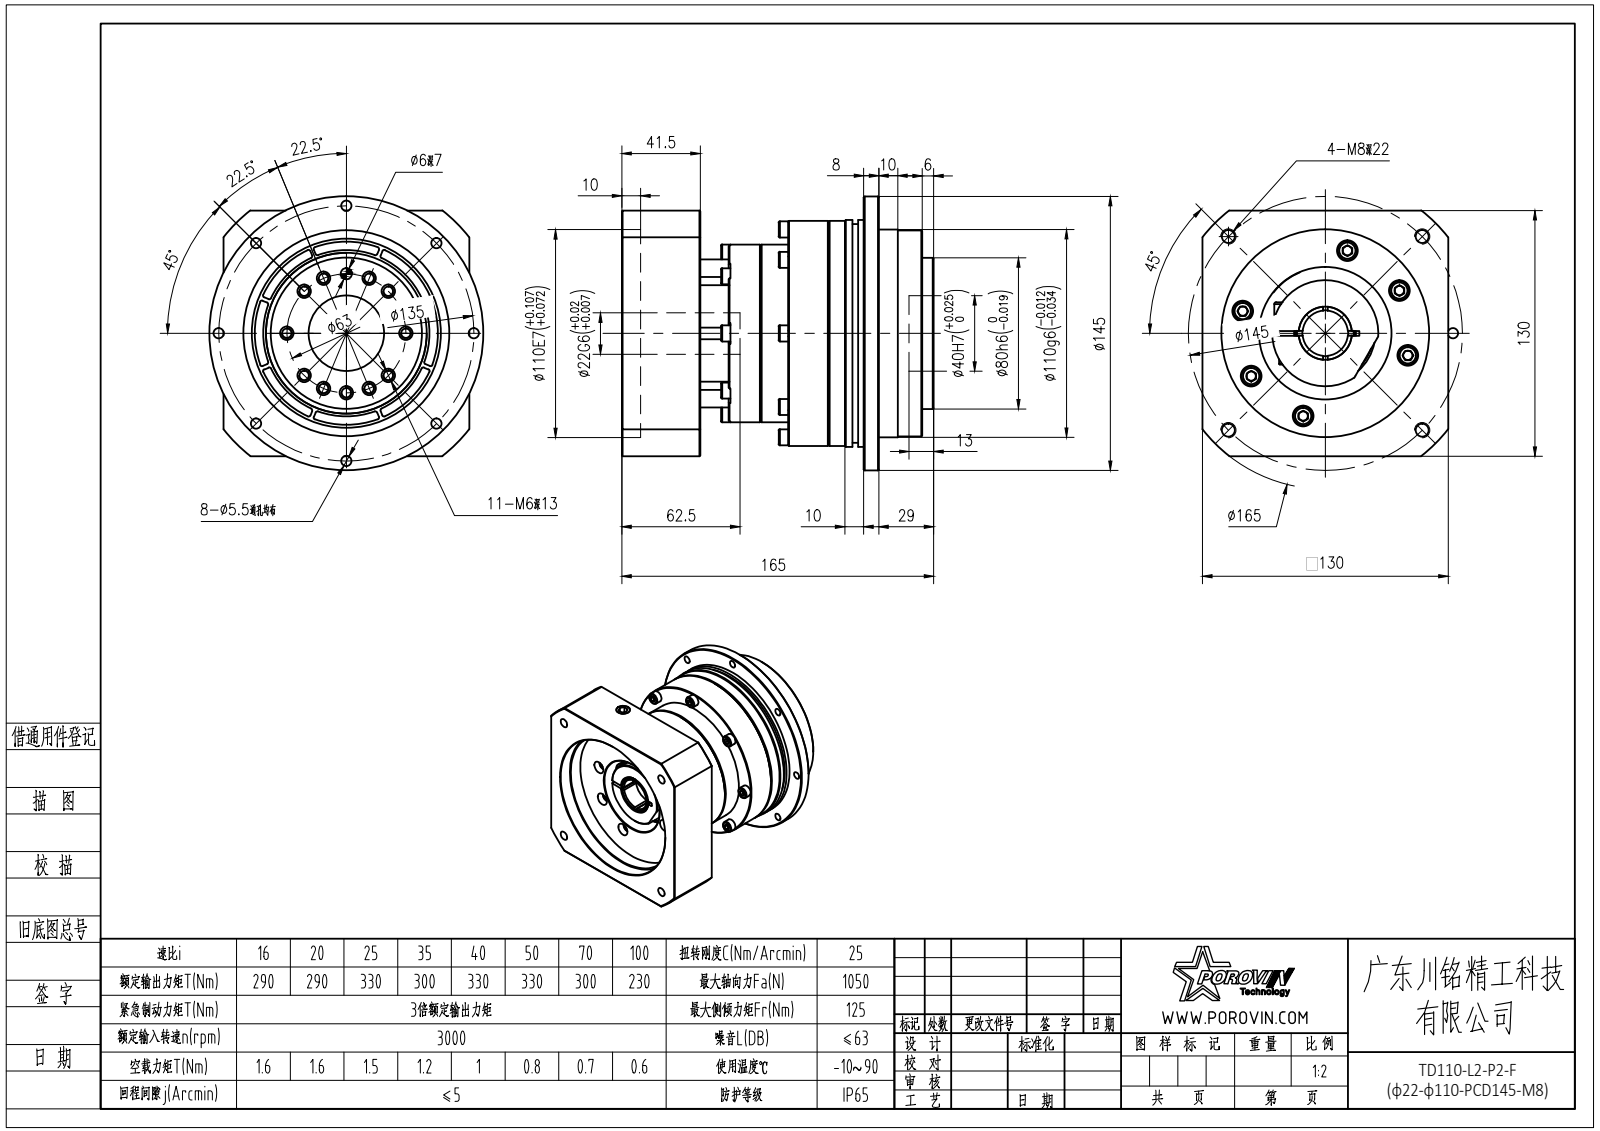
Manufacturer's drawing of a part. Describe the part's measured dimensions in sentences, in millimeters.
The part is named "二级齿圈外形图 KD110; hex socket set screws with flat point gb_GB_FASTENER_SCREWS_HSFP M12X12-N; spring lock washers--normal type gb_GB_FASTENER_WASHER_SW 5; hexagon socket head cap screws gb_GB_FASTENER_SCREWS_HSHCS M5X25-N (+3 more)". Its 3-D file was written by "SolidWorks 2016 (CONFIG_CONTROL_DESIGN)". It is 54 solids with 1422 faces: 610 planar, 530 cylindrical and 282 other. Overall it measures 165 by 145 by 145 millimeters. Its volume is 1 496 000 cubic millimeters and its surface area 234 702 square millimeters. Round holes: 30 of diameter 5.5, 22 of diameter 5.4, 12 of diameter 5, 11 of diameter 7, 6 of diameter 4.2, 6 of diameter 9.5, 4 of diameter 6.8, 1 of diameter 6, 1 of diameter 6.5, 1 of diameter 10.2, 1 of diameter 22, 1 of diameter 24. Round bosses or shafts: 22 of diameter 8.5, 22 of diameter 8, 22 of diameter 5, 1 of diameter 145, 1 of diameter 120, 1 of diameter 119, 1 of diameter 115.8, 1 of diameter 109. Partial cylindrical surfaces (rounded edges, fillets, slot ends): 32 of radius 1, 8 of radius 4.75, 1 of radius 5.5, 1 of radius 82.5. The main face-to-face distances are 68, 32, 36, 21.5, 130, 94.5, 20, 26.5, 62.5, 136. The hole center spacings are 74.49, 30.26, 47.99, 53.1, 68.73, 79.9, 102.3, 58.2.
